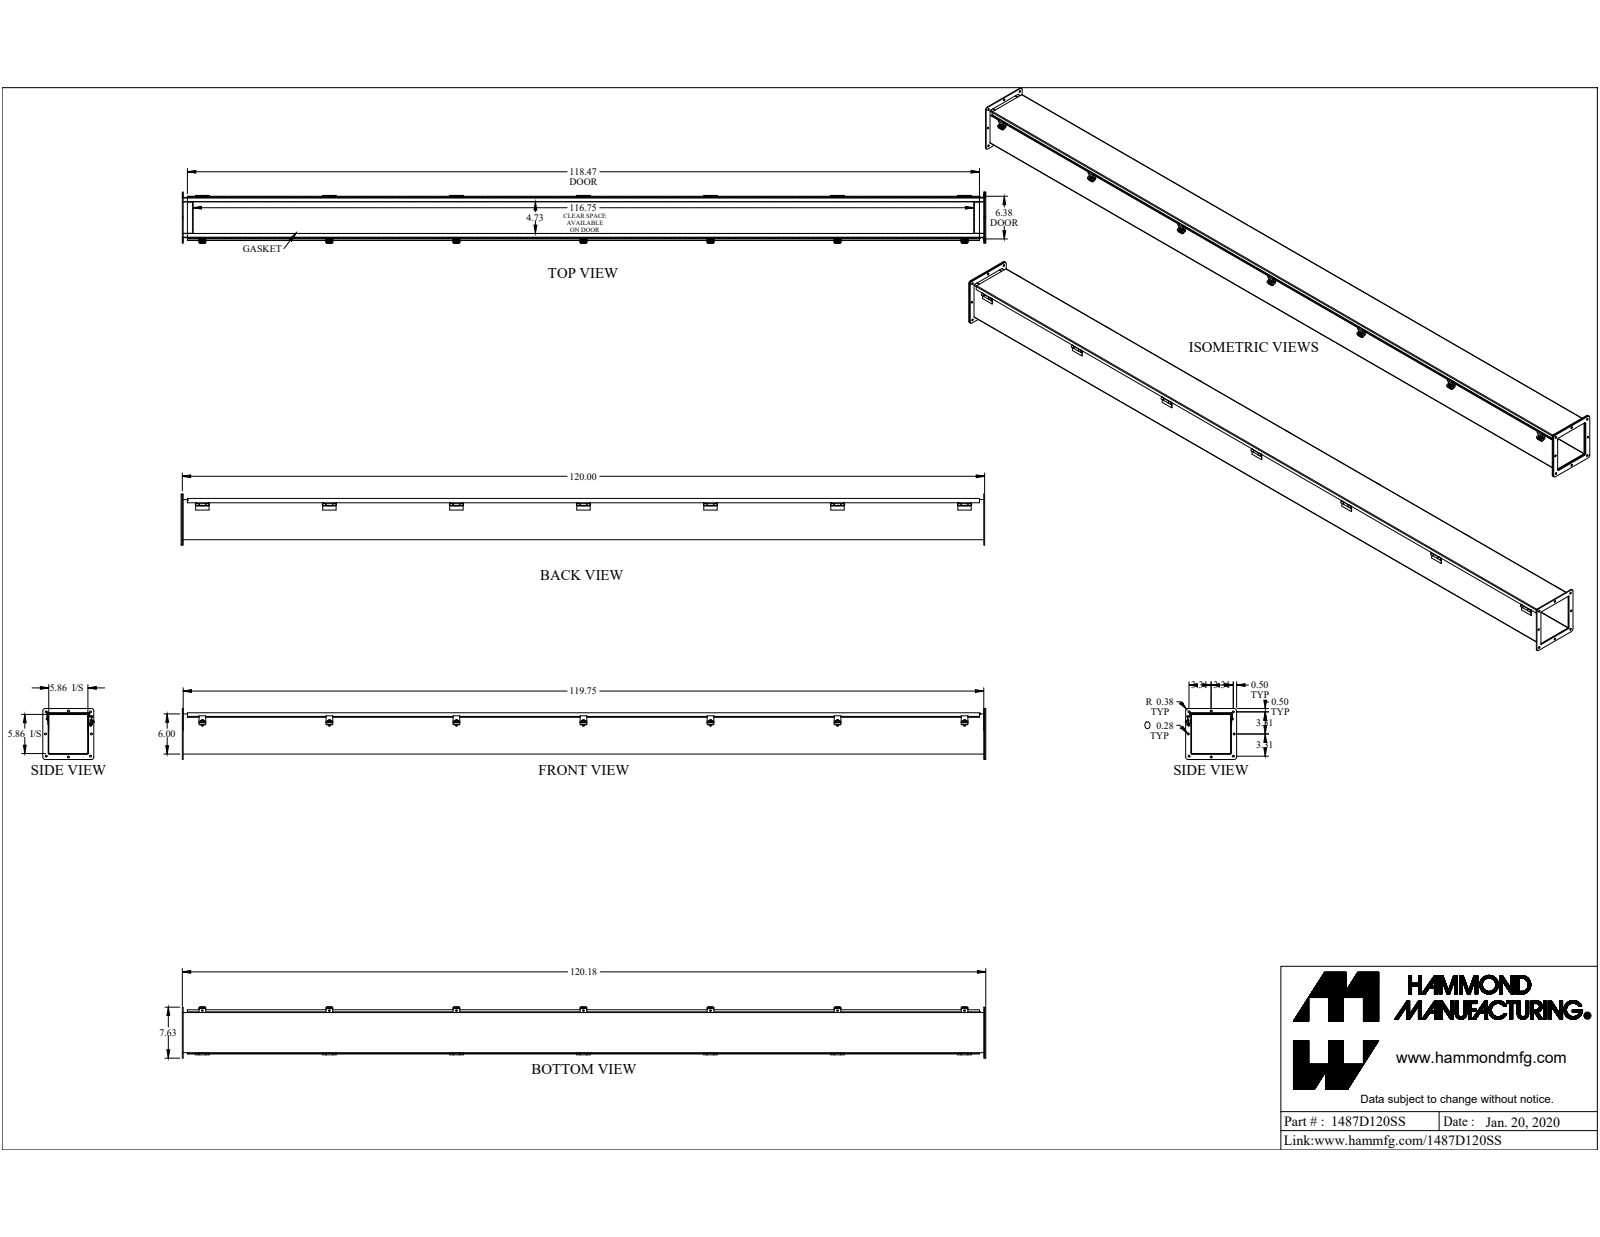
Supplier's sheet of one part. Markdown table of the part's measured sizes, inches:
| quantity | value |
| --- | --- |
| part name | 1487D120SS |
| STEP written by | SolidWorks 2019 (CONFIG_CONTROL_DESIGN) |
| units | inches |
| bodies | 60 solids, 1188 faces (766 planar, 323 cylindrical, 99 other) |
| overall size | 120.546 × 7.677 × 7.625 |
| volume | 277.1 in³ |
| surface area | 7 179 in² |
| round holes (diameter × count) | 0.281 × 8, 0.213 × 7, 0.187 × 1, 0.196 × 1, 0.258 × 1, 0.35 × 1 |
| round bosses / shafts (diameter × count) | 0.25 × 8, 0.48 × 7, 0.5 × 1, 0.337 × 1, 0.18 × 1 |
| partial cylindrical surfaces (radius × count) | 0.188 × 28, 0.03 × 14, 0.141 × 14, 0.375 × 8, 0.036 × 7, 0.108 × 7, 0.02 × 6, 0.063 × 4 |
| main face-to-face distances | 0.072, 5.928, 6.1, 6, 5.856, 6.172, 6.028, 0.187, 0.259, 0.172 |
| hole center spacings | 7.519, 3.315, 19, 38, 57, 76, 3.315, 4.861 |
